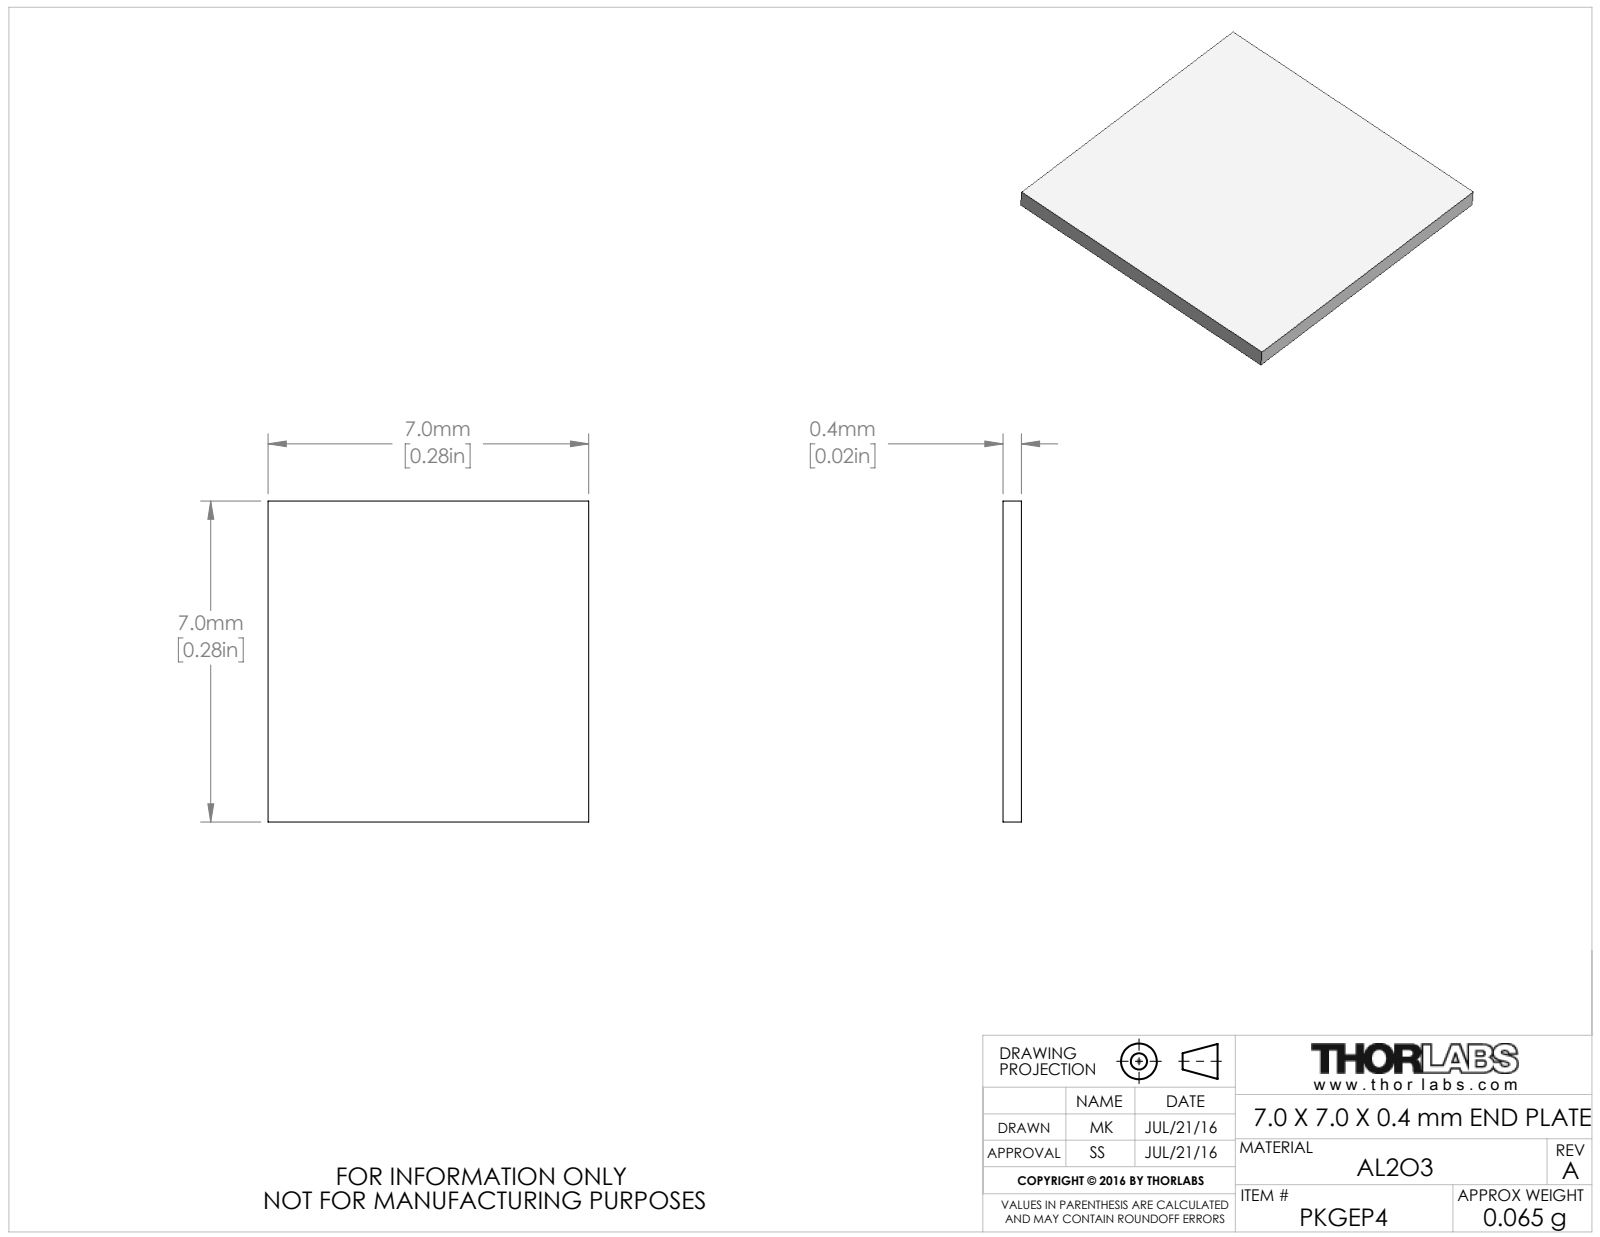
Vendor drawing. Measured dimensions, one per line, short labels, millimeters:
name: CTN002721
written by: SolidWorks 2016 (AUTOMOTIVE_DESIGN)
unit: mm
bodies: 1 solid, 6 faces (6 planar, 0 cylindrical, 0 other)
size: 7 × 7 × 0.4
volume: 20 mm³; area: 109 mm²
face distances: 0.4, 7
